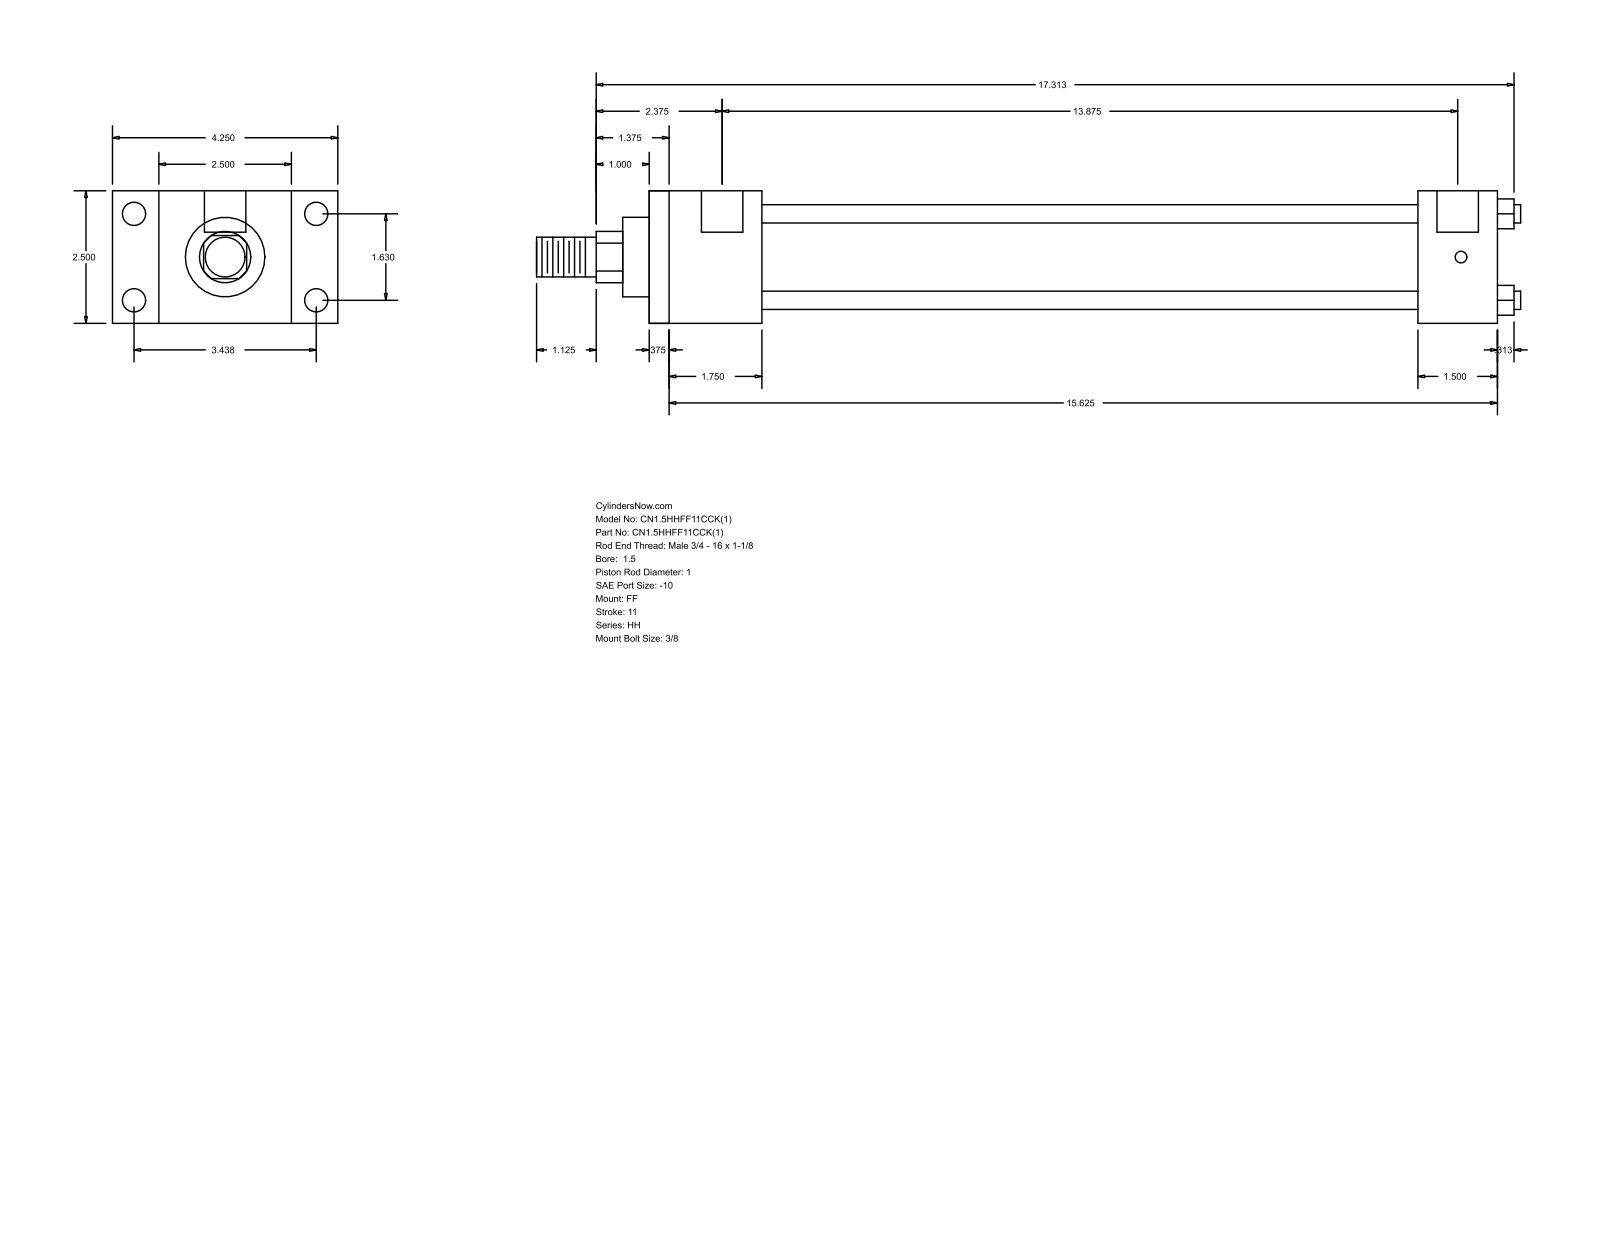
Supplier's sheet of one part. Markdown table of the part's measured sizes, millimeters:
| quantity | value |
| --- | --- |
| part name | HH_FF__0150_1 |
| STEP written by | GSSL Pune (CONFIG_CONTROL_DESIGN) |
| units | millimeters |
| bodies | 0 solids, 92 faces (64 planar, 28 cylindrical, 0 other) |
| overall size | 471.49 × 107.95 × 63.5 |
| round holes (diameter × count) | 5.56 × 4, 11.13 × 4, 19.84 × 2 |
| round bosses / shafts (diameter × count) | 8.76 × 4, 44.45 × 1, 38.1 × 1, 25.4 × 1, 19.05 × 1 |
| partial cylindrical surfaces (radius × count) | 12.29 × 1 |
| main face-to-face distances | 63.5, 406.4, 9.52, 396.88, 38.1, 53.98, 44.46, 352.42, 368.3, 358.78 |
| hole center spacings | 1.59, 41.4, 87.32, 96.64, 354.01, 355.6, 352.42 |
